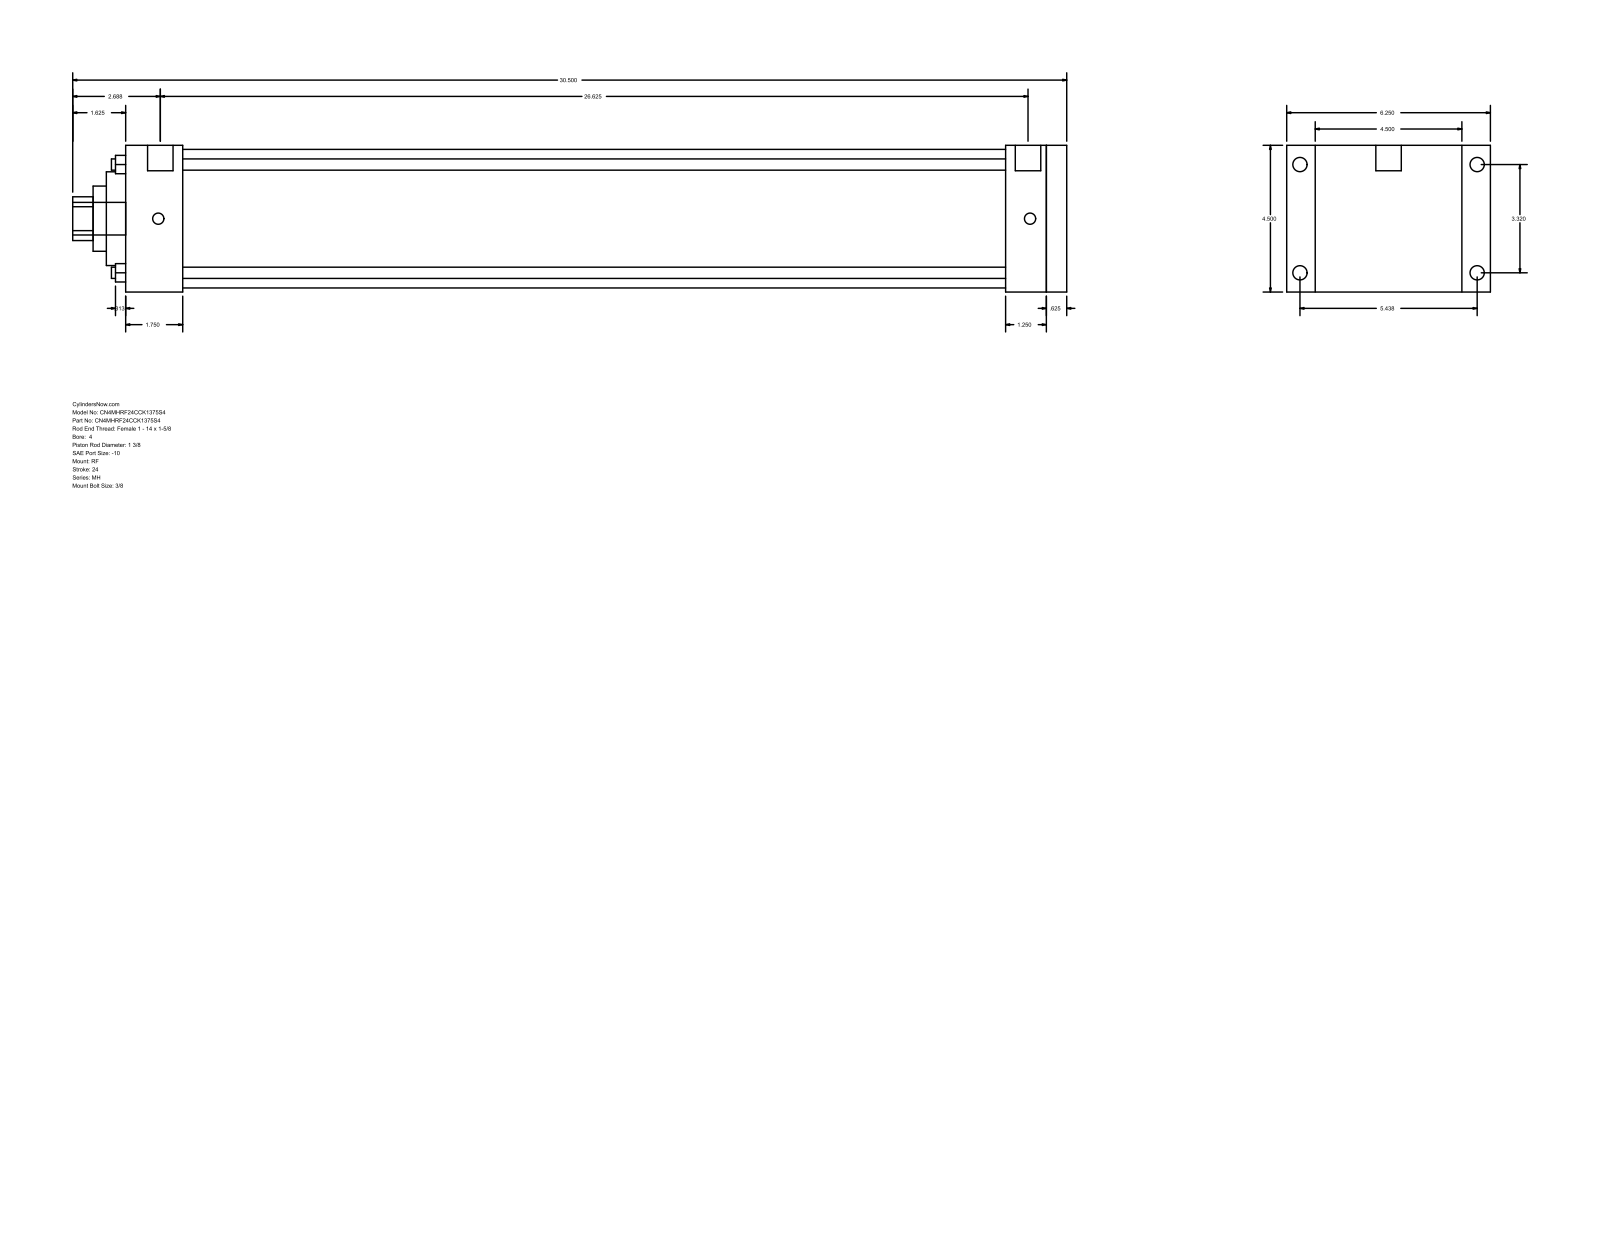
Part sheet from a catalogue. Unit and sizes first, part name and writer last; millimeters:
Units: millimetres
Overall size (bounding box): 774.7 × 158.75 × 114.3
Round holes (diameter × count): ⌀8.76 ×4, ⌀34.92 ×1, ⌀50.8 ×1, ⌀73.03 ×1, ⌀107.95 ×1
Round bosses / shafts (diameter × count): ⌀11.13 ×4, ⌀8.73 ×4, ⌀19.84 ×2, ⌀25.4 ×1
Partial cylindrical surfaces — rounded edges, fillets, slot ends (radius × count): R17.06 ×1
Main face-to-face distances: 114.3, 733.43, 717.56, 15.87, 44.45, 673.11, 688.98, 685.81, 641.36, 31.75
Hole centre spacings: 59.62, 84.32, 119.25
Bodies: 0 solids, 94 faces (65 planar, 29 cylindrical, 0 other)
Part name (STEP PRODUCT): MH_RF__0400_1.375
STEP written by: GSSL Pune (CONFIG_CONTROL_DESIGN)
